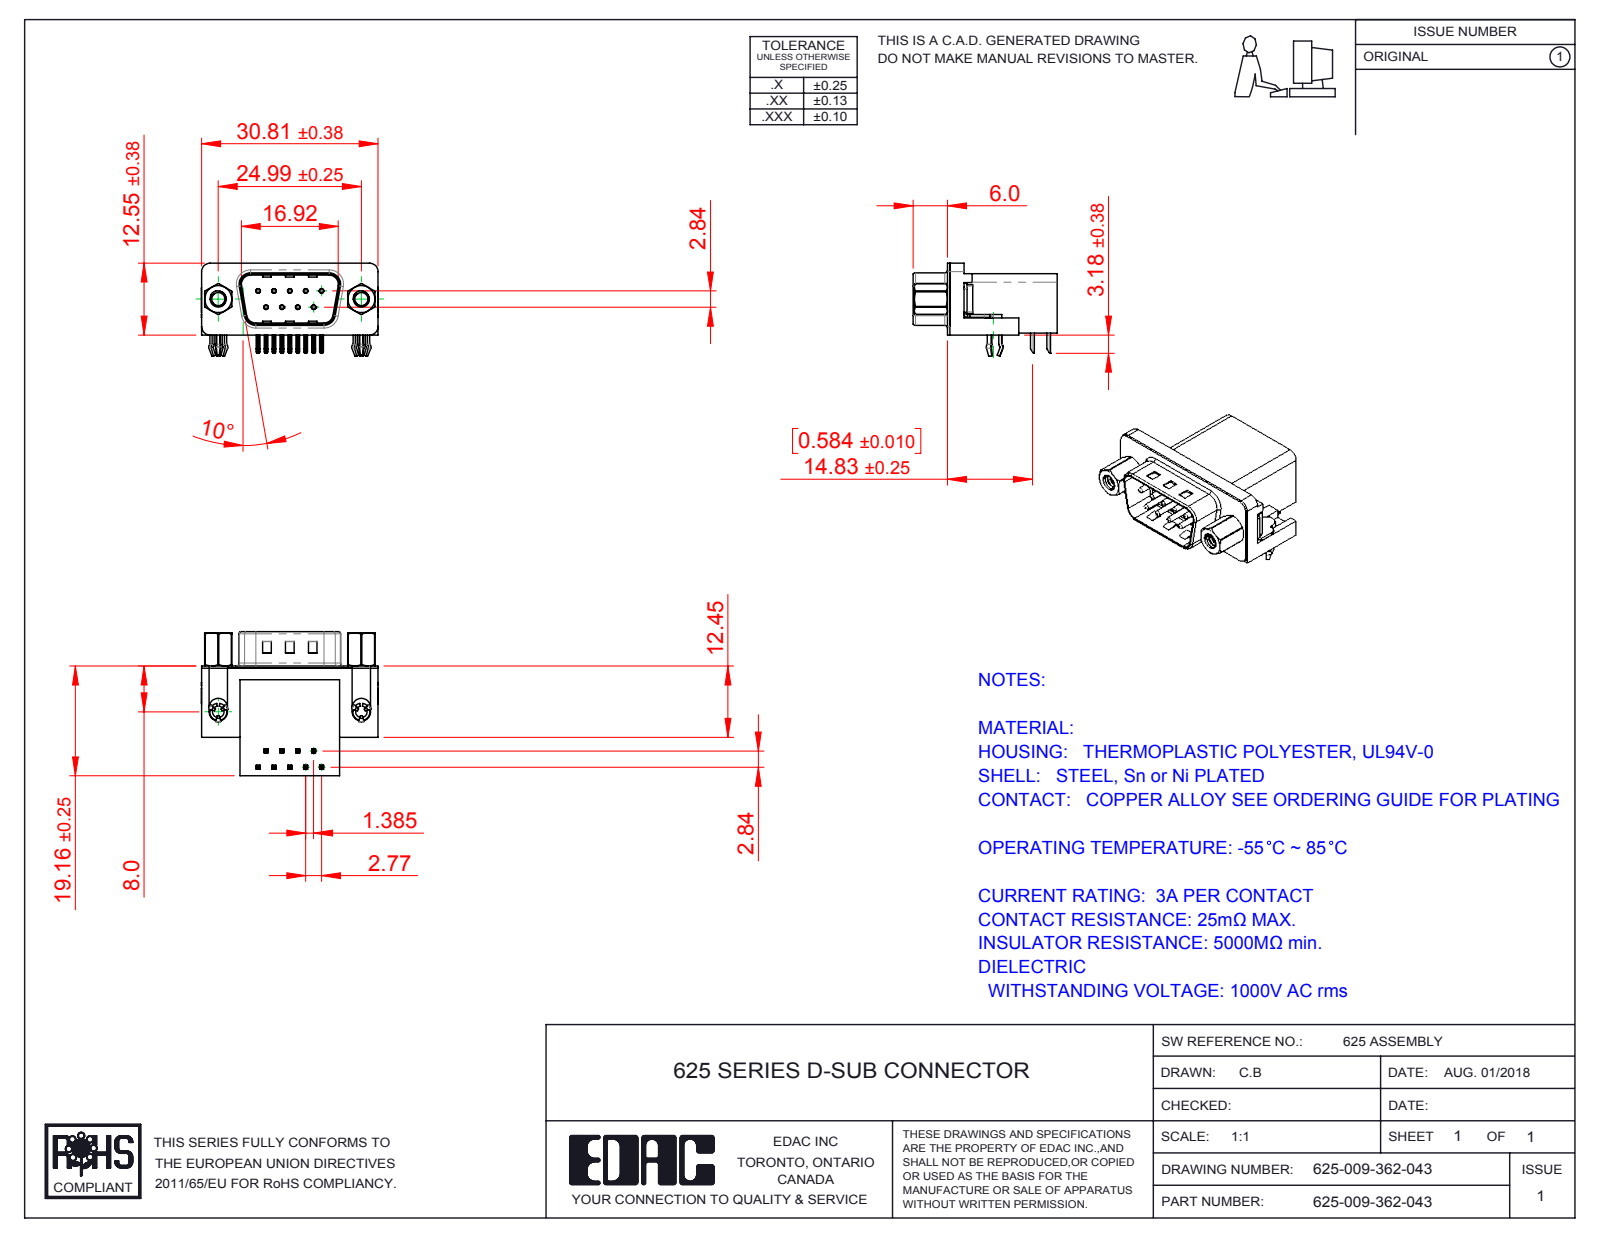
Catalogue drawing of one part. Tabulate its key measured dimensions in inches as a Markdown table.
| quantity | value |
| --- | --- |
| part name | 625 Contact Bottom; 625 Housing_9 Socket; 625 4-40 Threaded Rivet; 625 Contact Top (+4 more) |
| STEP written by | SolidWorks 2016 (CONFIG_CONTROL_DESIGN) |
| units | inches |
| bodies | 17 solids, 1223 faces (633 planar, 395 cylindrical, 195 other) |
| overall size | 1.216 × 0.991 × 0.64 |
| volume | 0.287 in³ |
| surface area | 8.517 in² |
| round holes (diameter × count) | 0.014 × 9, 0.031 × 9, 0.079 × 2, 0.089 × 2, 0.09 × 2, 0.157 × 2, 0.189 × 2, 0.197 × 2 |
| round bosses / shafts (diameter × count) | 0.03 × 9, 0.193 × 2, 0.187 × 2, 0.154 × 2, 0.118 × 2, 0.11 × 2 |
| partial cylindrical surfaces (radius × count) | 0.01 × 48, 0.005 × 18, 0.039 × 16, 0.02 × 9, 0.059 × 8, 0.063 × 8, 0.035 × 4, 0.079 × 4 |
| main face-to-face distances | 0.016, 0.407, 0.739, 0.754, 0.64, 0.098, 0.114, 0.014, 0.421, 0.264 |
| hole center spacings | 0.124, 0.109, 0.218, 0.198, 0.198, 0.327, 0.294, 0.295 |
